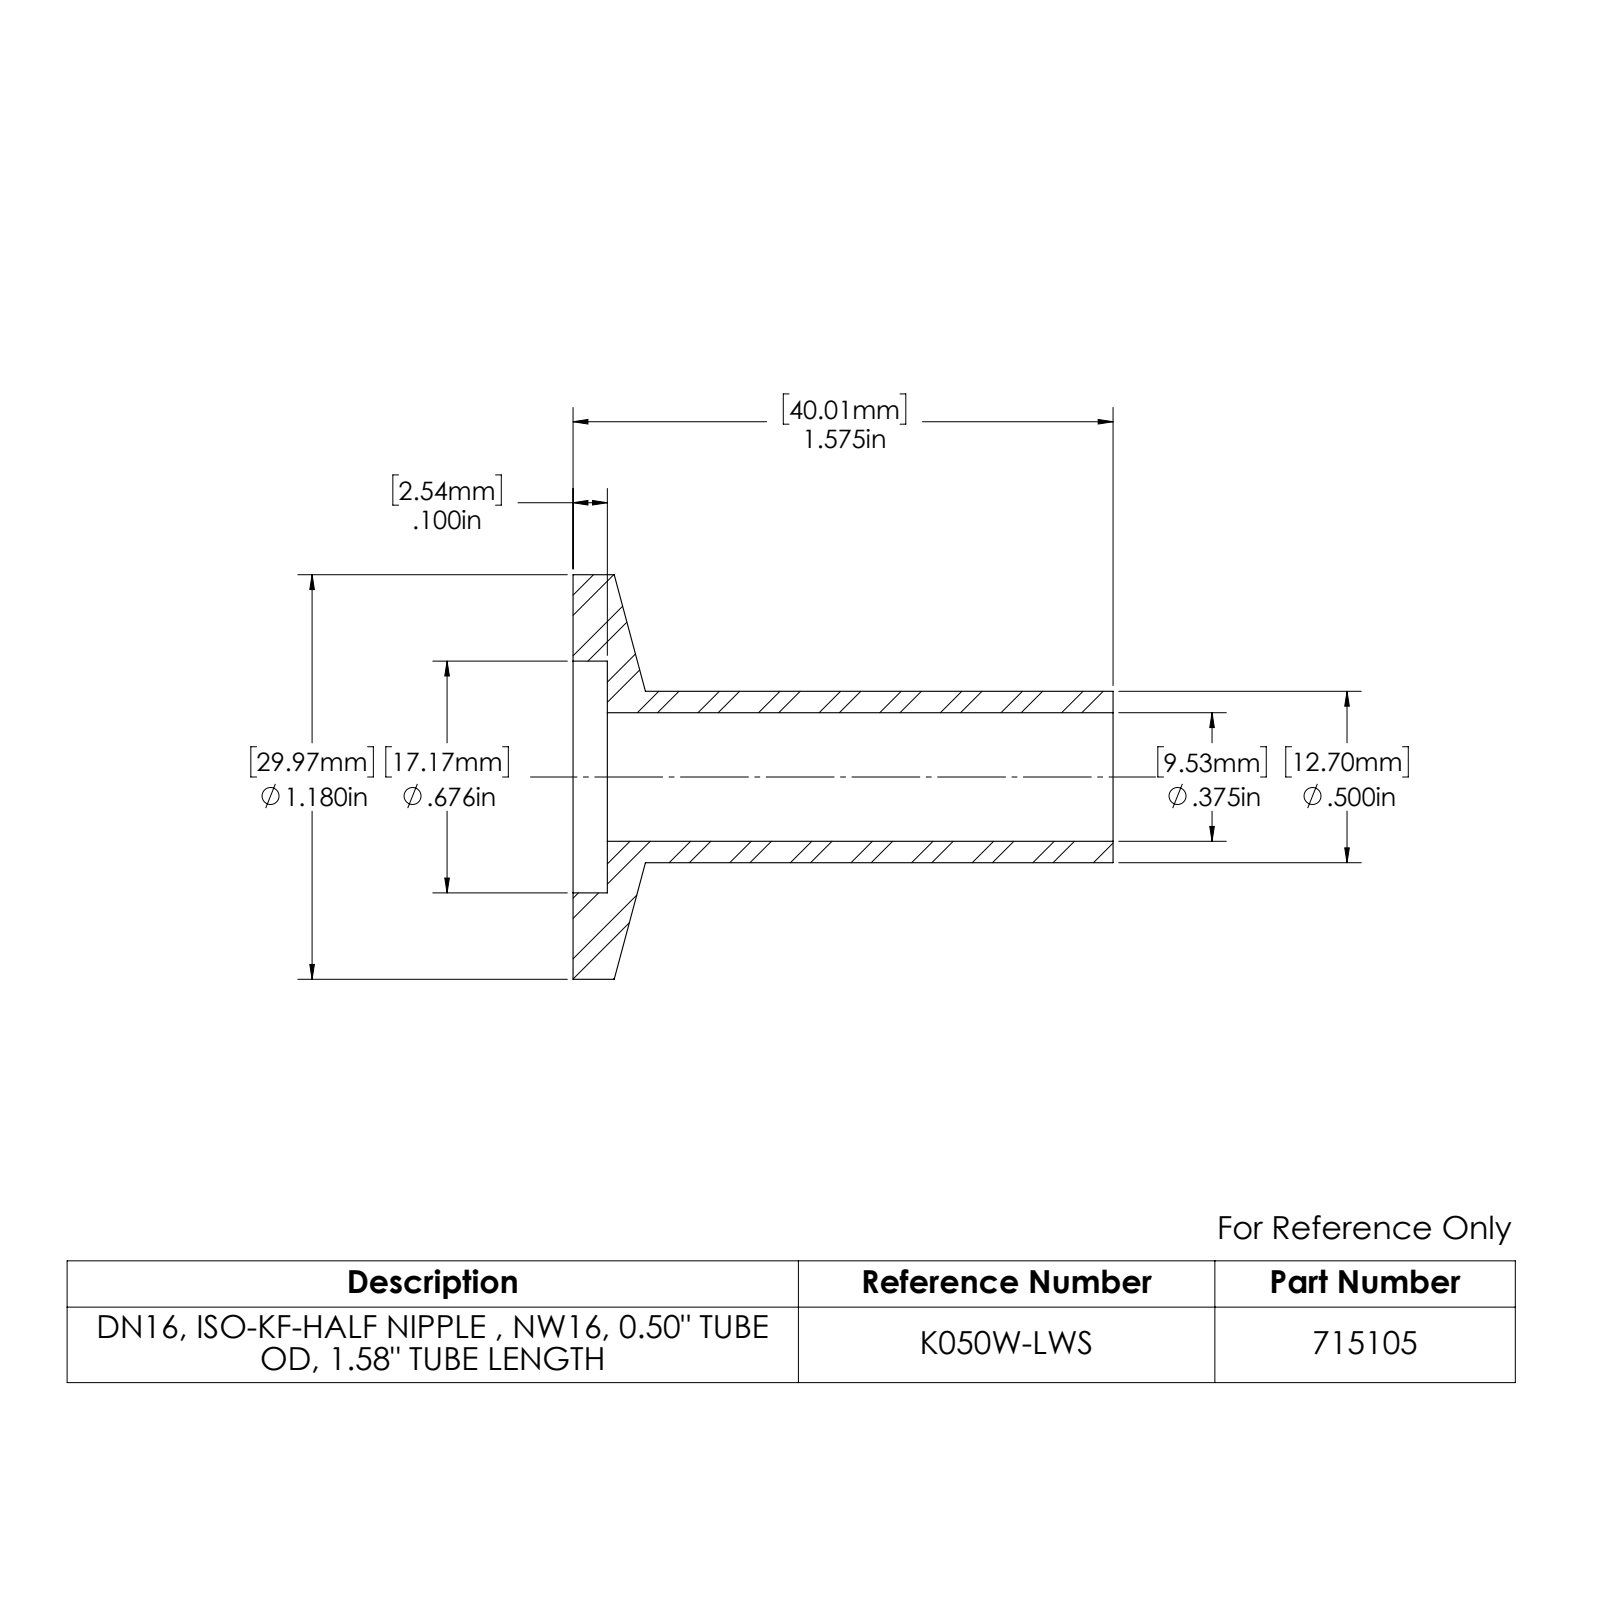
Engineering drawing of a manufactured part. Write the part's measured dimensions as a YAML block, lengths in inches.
part_name: "715105"
step_written_by: "SolidWorks 2022 (AUTOMOTIVE_DESIGN)"
units: inches
bodies: {solids: 1, faces: 13, planar: 3, cylindrical: 8, other: 2}
overall_size: [1.575, 1.18, 1.18]
volume: 0.253
surface_area: 6.535
round_holes:
  - {diameter: 0.375, count: 1}
  - {diameter: 0.676, count: 1}
round_bosses_or_shafts:
  - {diameter: 1.18, count: 1}
  - {diameter: 0.5, count: 1}
face_to_face_distances: [0.1, 1.575, 1.475]
